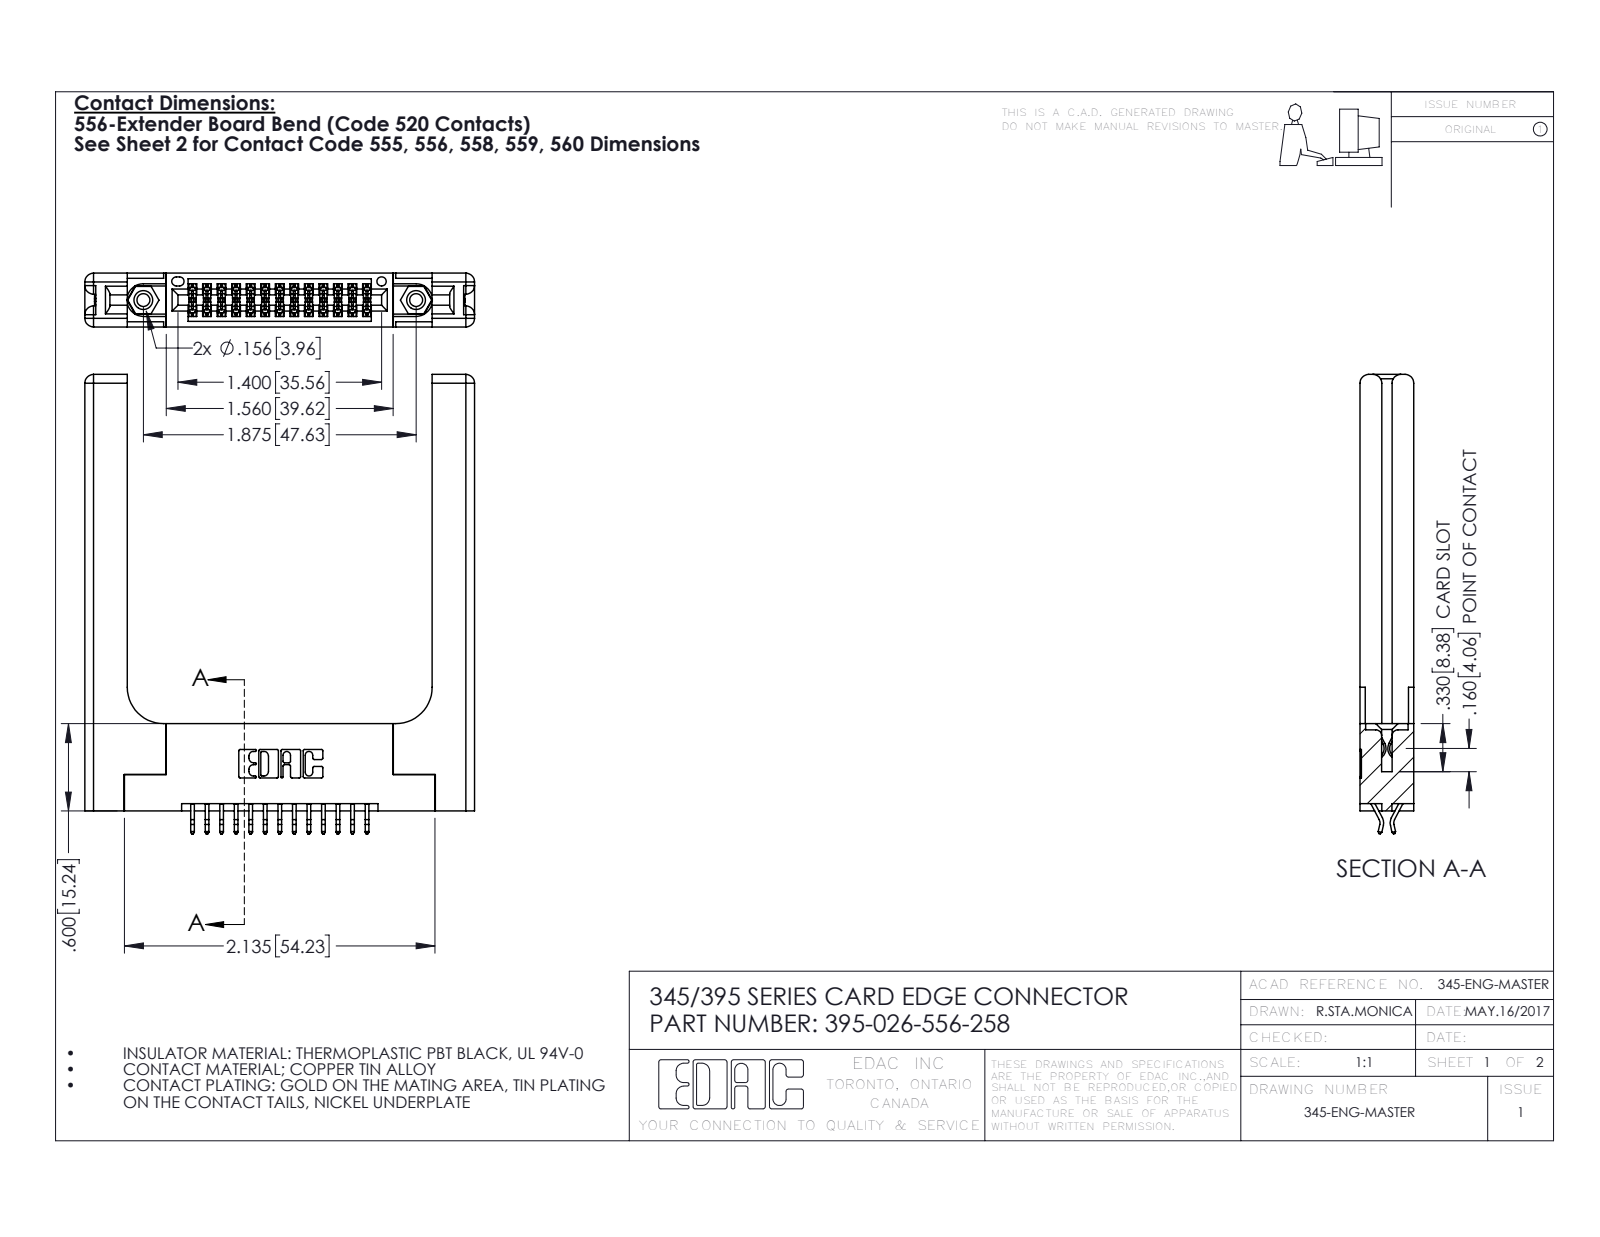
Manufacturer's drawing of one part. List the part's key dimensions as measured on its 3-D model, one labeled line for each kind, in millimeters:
Part name (STEP PRODUCT): 345-250-001_345-250-001-102; 345-292-001_556 Tail; 345-220-058_345-220-058; 345 Part_Flush Mounting Lugs - 0.156 Dia-TH (+1 more)
STEP written by: SolidWorks 2016 (CONFIG_CONTROL_DESIGN)
Units: millimetres
Bodies: 31 solids, 1838 faces (1190 planar, 588 cylindrical, 60 other)
Overall size (bounding box): 80.2 × 68 × 9.4
Volume: 14 800 mm³ · Surface area: 13 850 mm²
Round holes (diameter × count): ⌀2.3 ×2, ⌀3.2 ×2, ⌀4 ×2, ⌀1.6 ×1
Round bosses / shafts (diameter × count): ⌀3.9 ×2
Partial cylindrical surfaces — rounded edges, fillets, slot ends (radius × count): R0.2 ×39, R0.3 ×22, R1.5 ×16, R0.2 ×6, R0.8 ×6, R0.7 ×3, R0.3 ×2, R0.4 ×2
Main face-to-face distances: 9.4, 1.8, 7.6, 2, 3.8, 3.8, 5.6, 5.1, 5.7, 53.2
Hole centre spacings: 6.9, 41.7, 47.6
